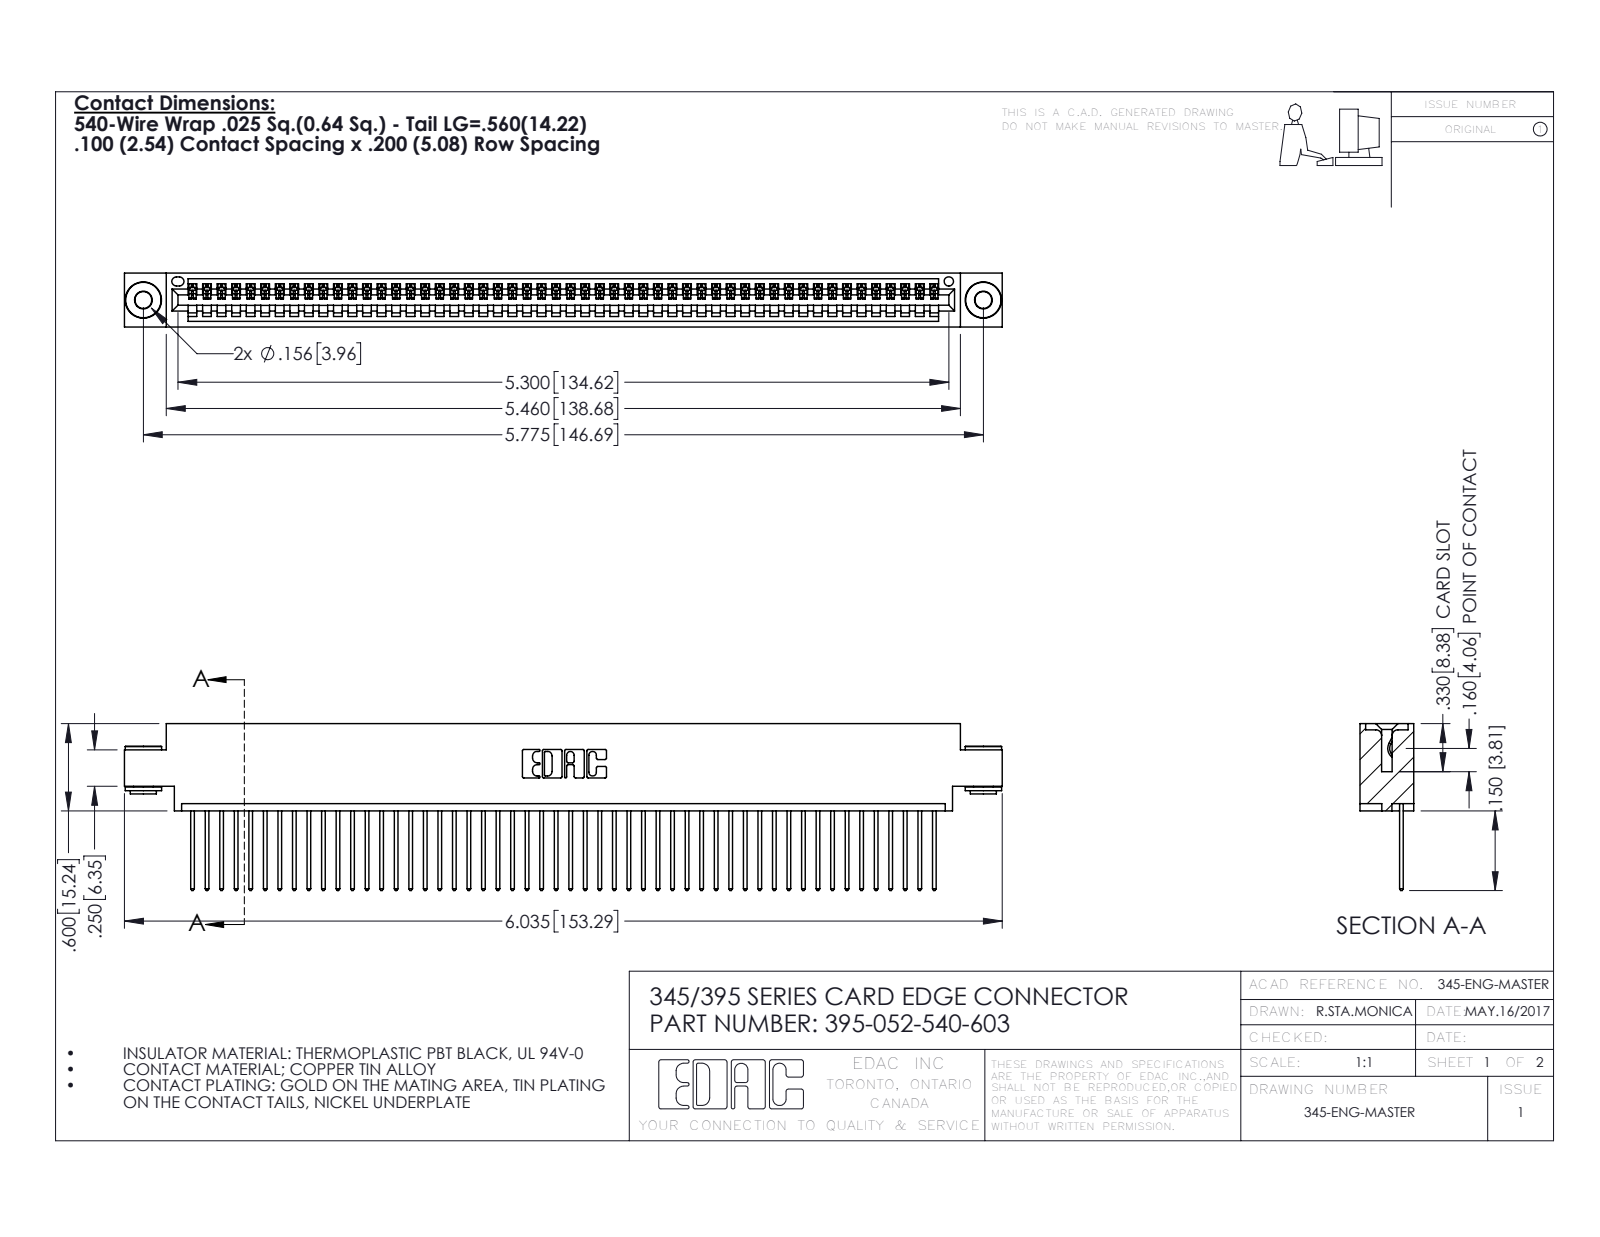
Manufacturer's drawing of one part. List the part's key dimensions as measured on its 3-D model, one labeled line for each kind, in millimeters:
Part name (STEP PRODUCT): 345-250-002_345-250-002-102; 345-292-001_345-293-140; 345 Part_0.170 Offset - 0.156 Dia-TH; 395-052-540-603
STEP written by: SolidWorks 2016 (CONFIG_CONTROL_DESIGN)
Units: millimetres
Bodies: 55 solids, 3184 faces (2174 planar, 1002 cylindrical, 8 other)
Overall size (bounding box): 153.3 × 29.1 × 9.4
Volume: 14 600 mm³ · Surface area: 20 410 mm²
Round holes (diameter × count): ⌀2.9 ×2, ⌀4 ×2, ⌀1.6 ×1
Round bosses / shafts (diameter × count): ⌀6.4 ×2, ⌀4.6 ×2, ⌀3.5 ×2
Partial cylindrical surfaces — rounded edges, fillets, slot ends (radius × count): R0.2 ×104, R0.3 ×104, R0.3 ×22, R0.2 ×6, R0.8 ×6, R0.7 ×3, R0.8 ×2, R1 ×2
Main face-to-face distances: 1.8, 7.6, 9.4, 2.5, 6.9, 0.6, 5.1, 5.7, 4.4, 3.8
Hole centre spacings: 6.9, 140.7, 146.7
